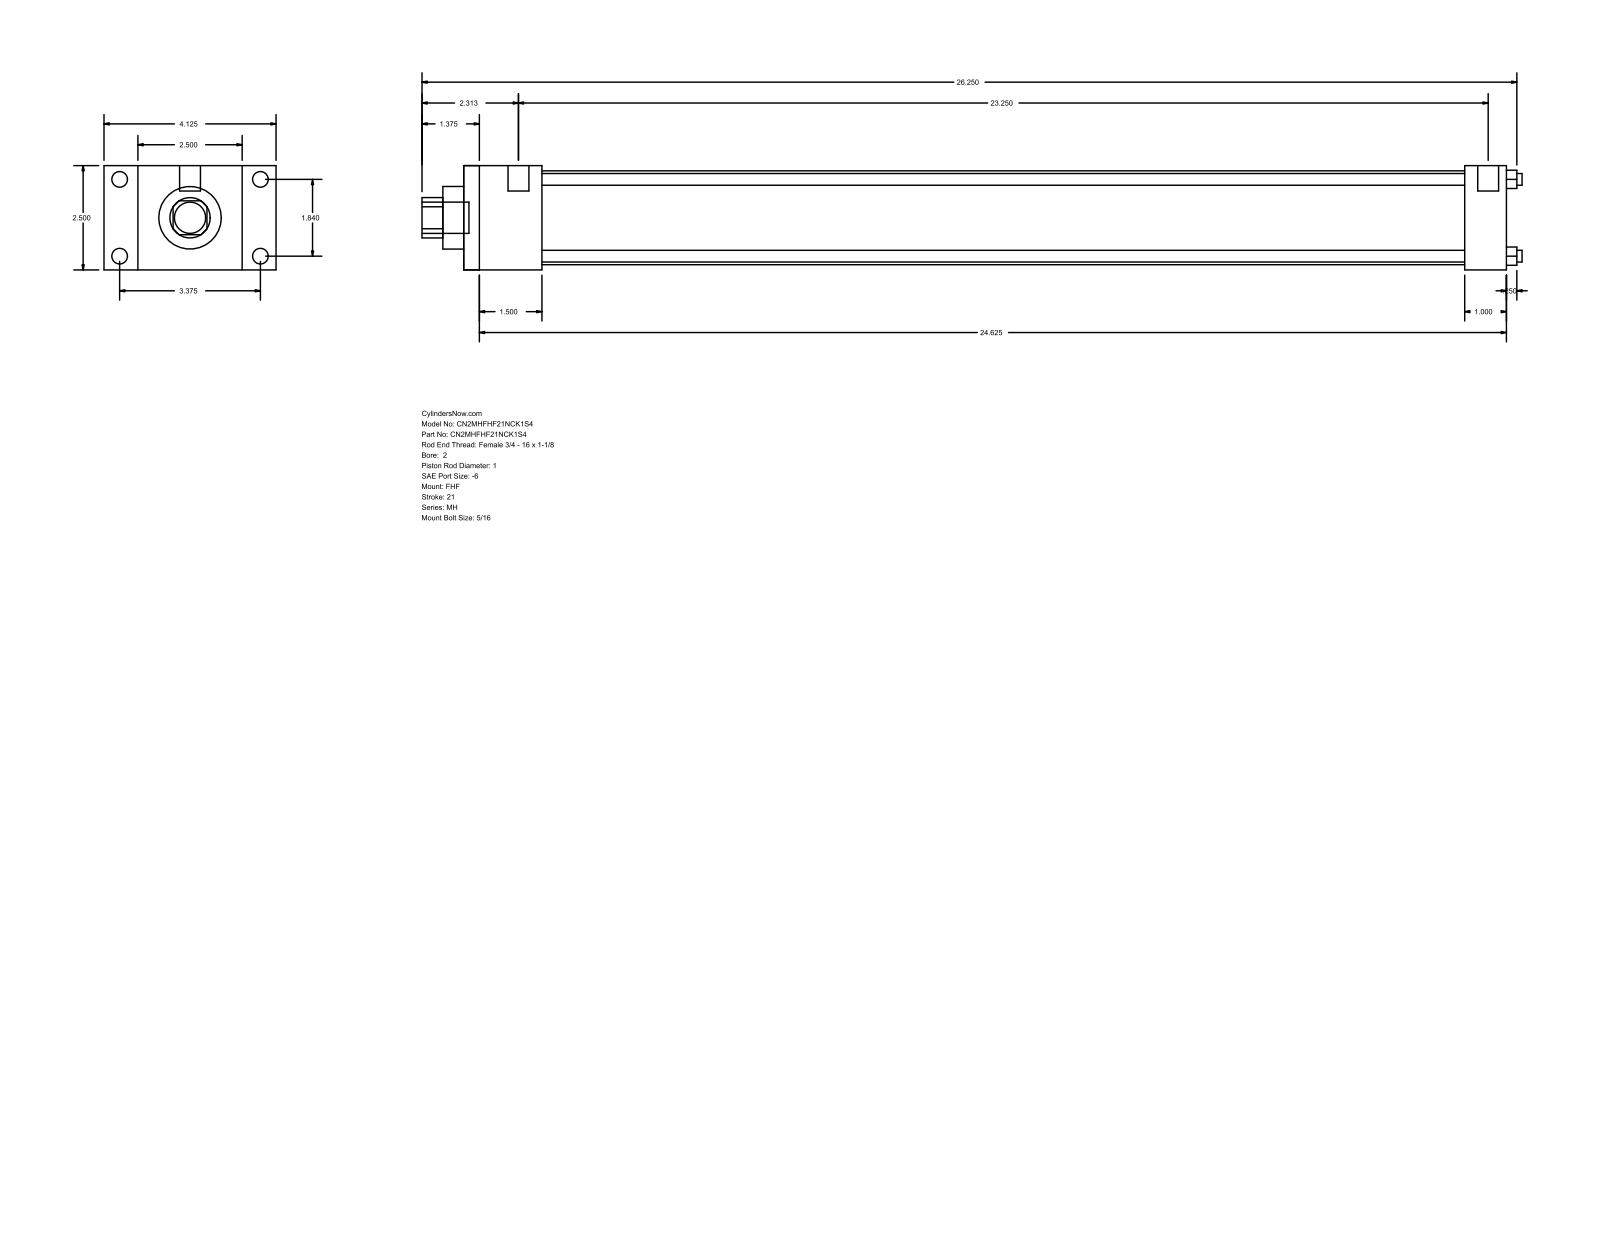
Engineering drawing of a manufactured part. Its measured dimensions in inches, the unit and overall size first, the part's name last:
Units: inches
Overall size (bounding box): 26.375 × 4.125 × 2.5
Round holes (diameter × count): ⌀0.281 ×4, ⌀1 ×1, ⌀1.5 ×1, ⌀2.25 ×1
Round bosses / shafts (diameter × count): ⌀0.375 ×4, ⌀0.219 ×4, ⌀0.5 ×2, ⌀0.75 ×1
Partial cylindrical surfaces — rounded edges, fillets, slot ends (radius × count): R0.484 ×1
Main face-to-face distances: 2.5, 25, 1.875, 23.125, 0.813, 3.313, 4.125, 1, 24, 22.125
Hole centre spacings: 1.301, 1.84, 2.602
Bodies: 0 solids, 88 faces (60 planar, 28 cylindrical, 0 other)
Part name (STEP PRODUCT): MH_FHF__0200_1
STEP written by: GSSL Pune (CONFIG_CONTROL_DESIGN)
